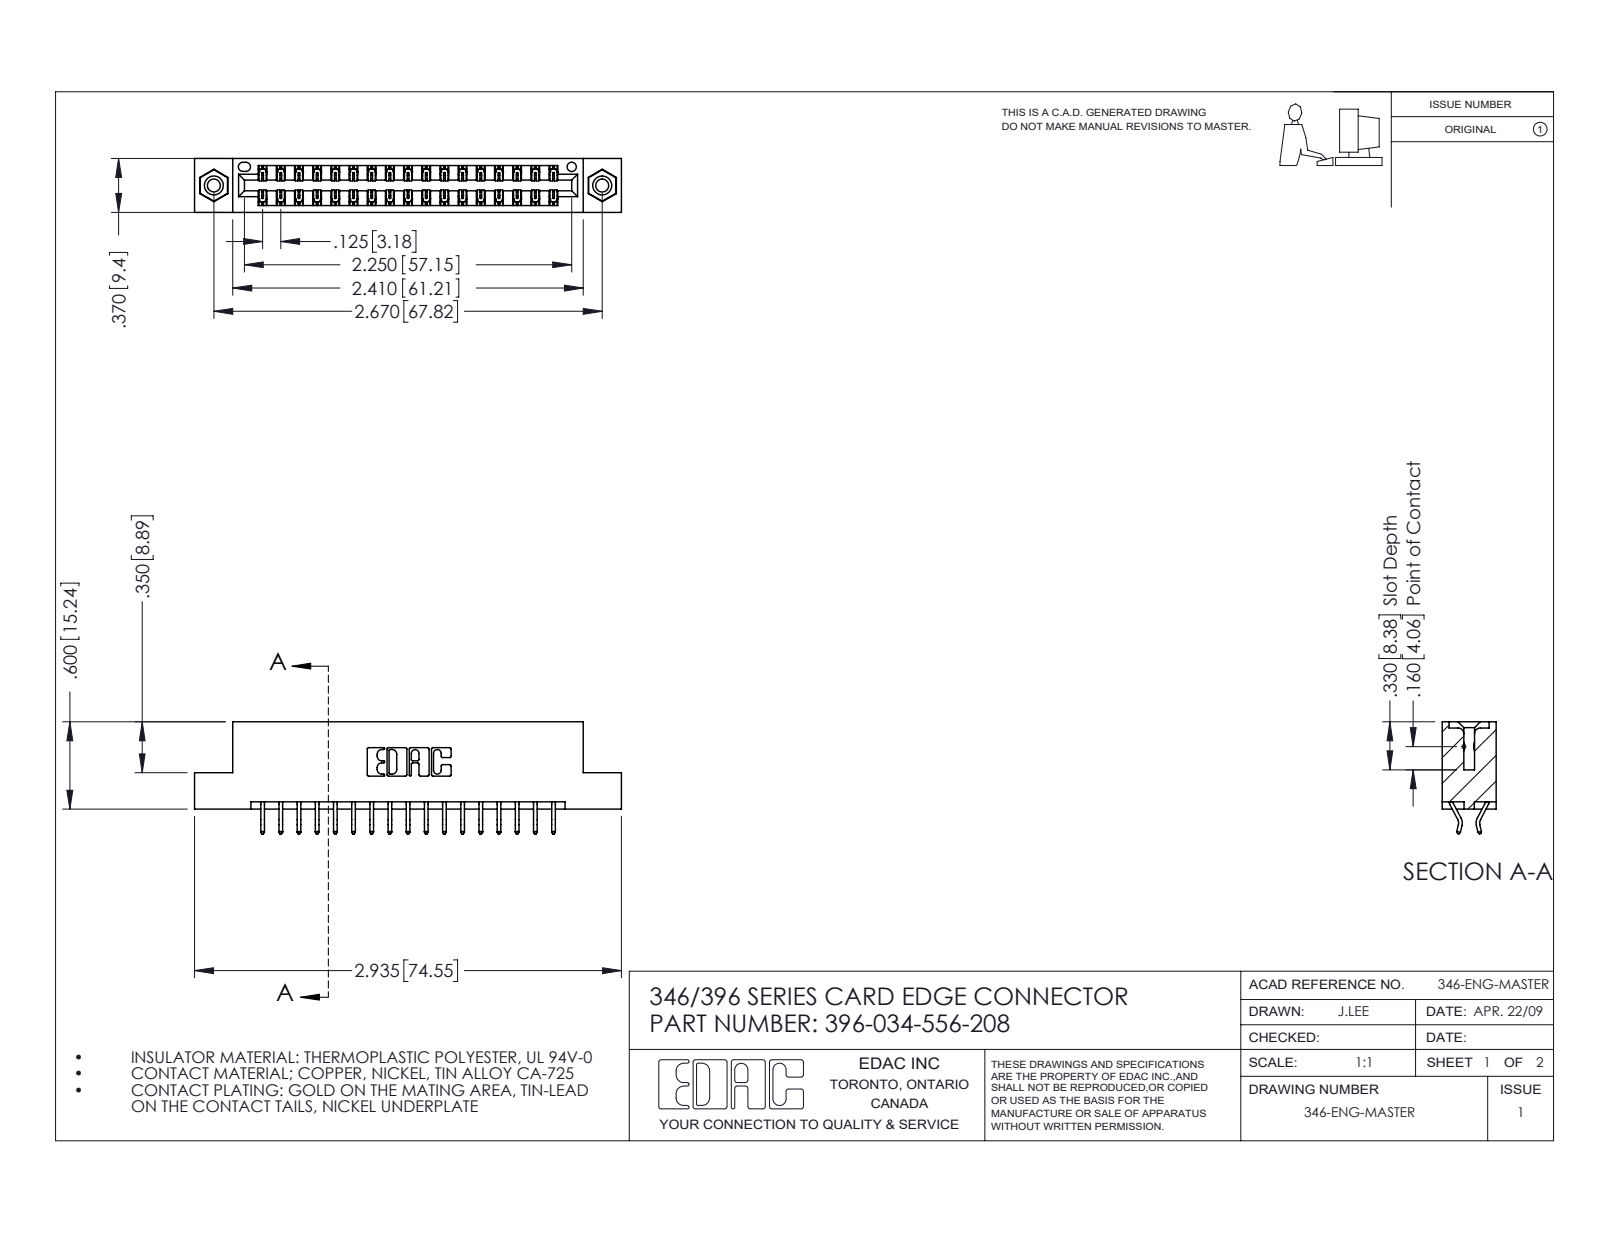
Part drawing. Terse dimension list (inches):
name: 346 Part_Flush Mounting Lugs - 0.156 Dia-TI; 396-034-556-208; 345-250-001_345-250-003-102; 345-292-001_556 Tail
written by: SolidWorks 2016 (CONFIG_CONTROL_DESIGN)
unit: in
bodies: 37 solids, 2154 faces (1434 planar, 704 cylindrical, 16 other)
size: 2.935 × 0.77 × 0.37
volume: 0.431 in³; area: 14.43 in²
holes: 2× ⌀0.089, 2× ⌀0.125, 2× ⌀0.156, 1× ⌀0.064
bosses: 2× ⌀0.155
rounds: 51× R0.006, 22× R0.01, 6× R0.007, 6× R0.031, 3× R0.026, 2× R0.01, 2× R0.014, 2× R0.022
face distances: 0.048, 0.322, 0.25, 0.37, 0.025, 0.072, 0.298, 0.275, 0.148, 0.222
hole spacings: 0.246, 2.463, 2.67
